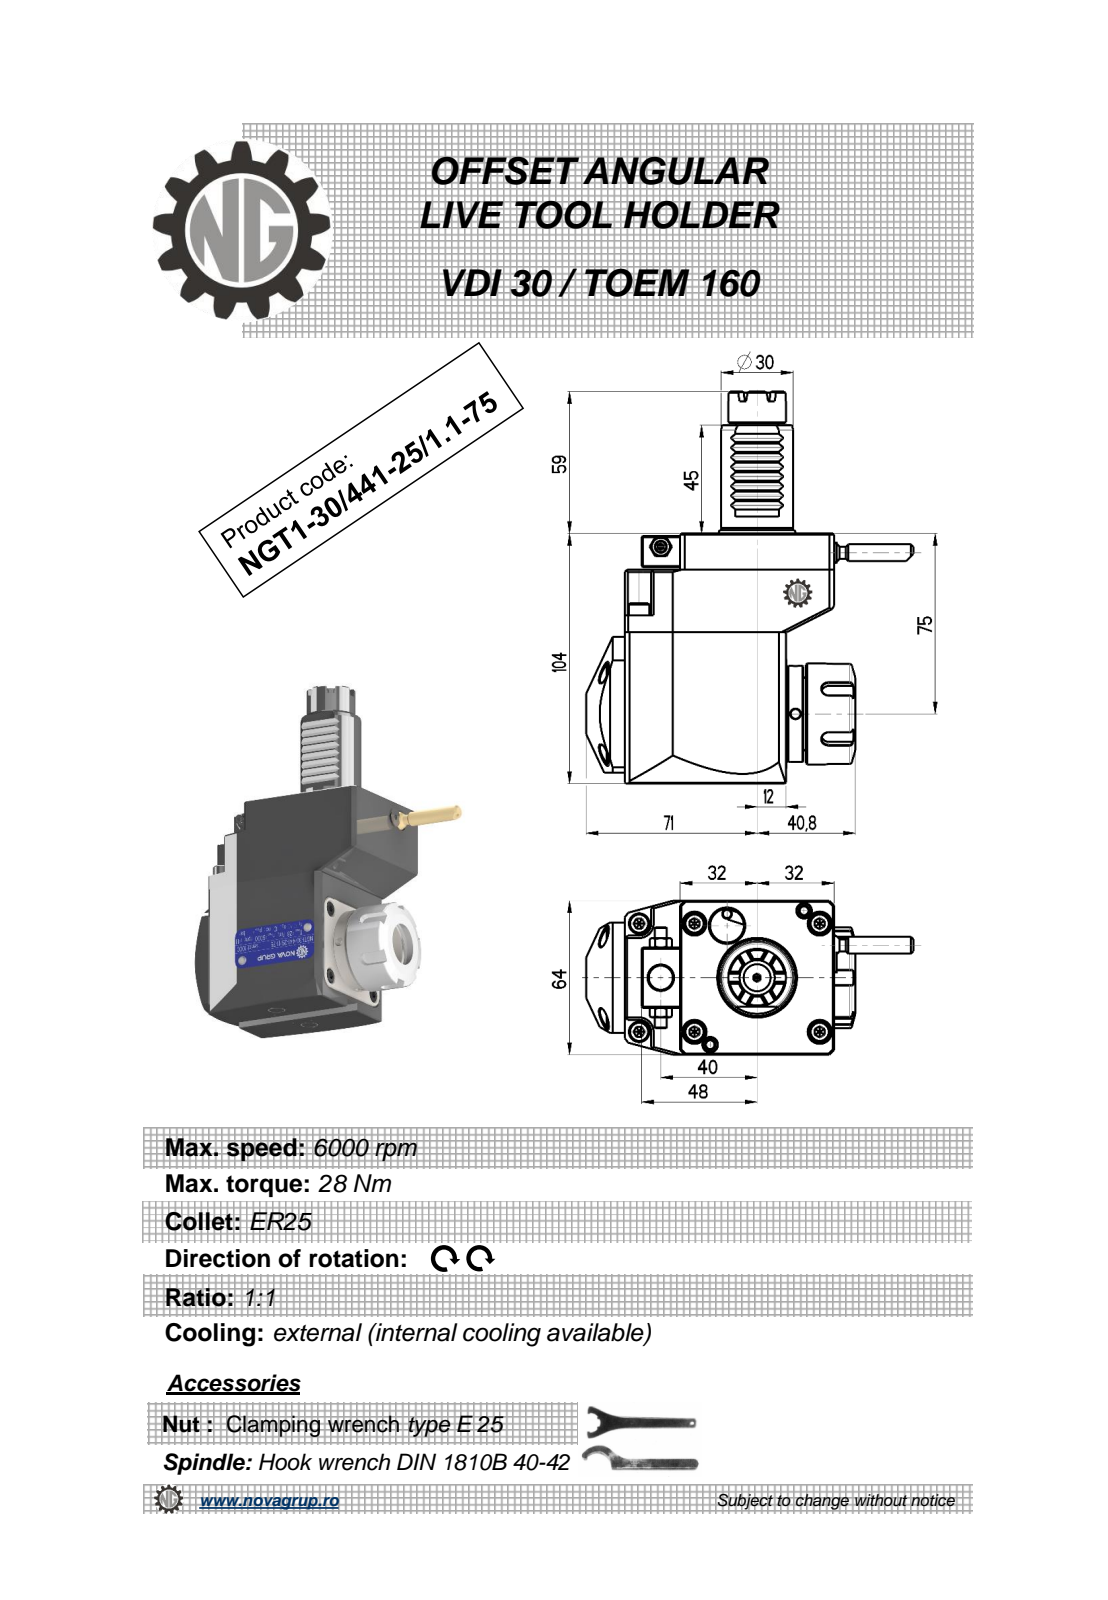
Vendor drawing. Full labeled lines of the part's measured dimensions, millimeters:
Part name (STEP PRODUCT): NGT1_30_441_25_1_1_75
STEP written by: PRO/ENGINEER BY PARAMETRIC TECHNOLOGY CORPORATION, 2010280 (CONFIG_CONTROL_DESIGN)
Units: millimetres
Bodies: 1 solid, 487 faces (240 planar, 92 cylindrical, 155 other)
Overall size (bounding box): 163 × 135.88 × 65.4
Volume: 557 999 mm³ · Surface area: 54 002 mm²
Round holes (diameter × count): ⌀4 ×2, ⌀2.5 ×1, ⌀3 ×1, ⌀4.2 ×1, ⌀9.5 ×1, ⌀10 ×1, ⌀20.3 ×1
Round bosses / shafts (diameter × count): ⌀8.96 ×2, ⌀5 ×2, ⌀42 ×1, ⌀40 ×1, ⌀33 ×1, ⌀30 ×1, ⌀24 ×1, ⌀17.7 ×1
Partial cylindrical surfaces — rounded edges, fillets, slot ends (radius × count): R0.26 ×12, R0.3 ×8, R3 ×5, R3.5 ×4, R4 ×2, R32 ×1
Main face-to-face distances: 64, 104, 87, 67.2, 19.8, 20, 15, 89, 67, 1
Hole centre spacings: 13.54, 55.95, 68, 68.35, 89.22
